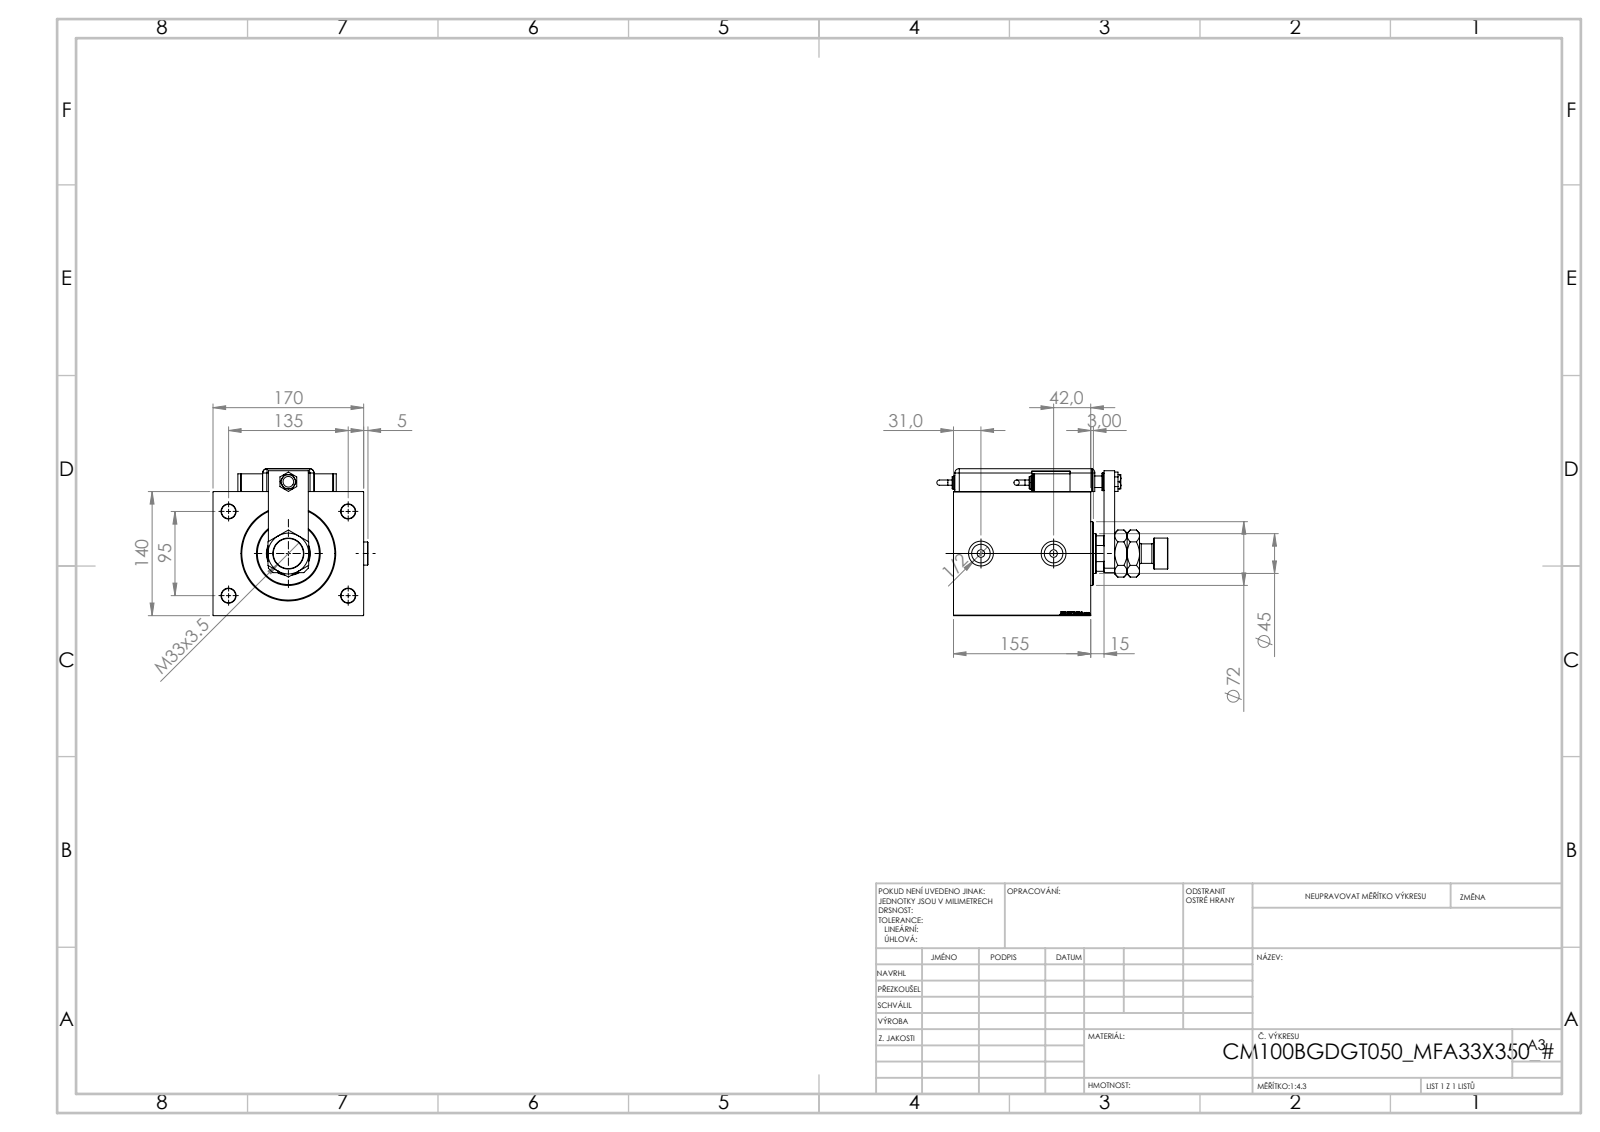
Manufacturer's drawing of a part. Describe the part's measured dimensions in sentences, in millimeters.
The part is named "Zatka_OIL_PORT; NUT_D19; SWITCH_Q_FRONT_BACK; MAGNETIC SWITCH Q (+8 more)". Its 3-D file was written by "SolidWorks 2019 (CONFIG_CONTROL_DESIGN)". It is 16 solids with 1374 faces: 658 planar, 131 cylindrical and 585 other. Overall it measures 260.76 by 174.9 by 165.8 millimeters. Its volume is 3 579 000 cubic millimeters and its surface area 365 465 square millimeters. Round holes: 4 of diameter 16, 2 of diameter 4, 2 of diameter 8, 2 of diameter 8.5, 2 of diameter 20.96, 2 of diameter 28, 1 of diameter 12, 1 of diameter 13, 1 of diameter 14, 1 of diameter 31.5, 1 of diameter 33, 1 of diameter 45. Round bosses or shafts: 3 of diameter 20, 2 of diameter 26, 2 of diameter 16, 2 of diameter 14, 2 of diameter 6, 1 of diameter 72, 1 of diameter 35, 1 of diameter 22. Partial cylindrical surfaces (rounded edges, fillets, slot ends): 9 of radius 5, 1 of radius 10, 1 of radius 22. The main face-to-face distances are 140, 170, 155, 3, 26, 129, 15, 114, 1.5, 25.8. The hole center spacings are 82.54, 75.36, 95, 135, 145.15, 165.08, 20, 81.
